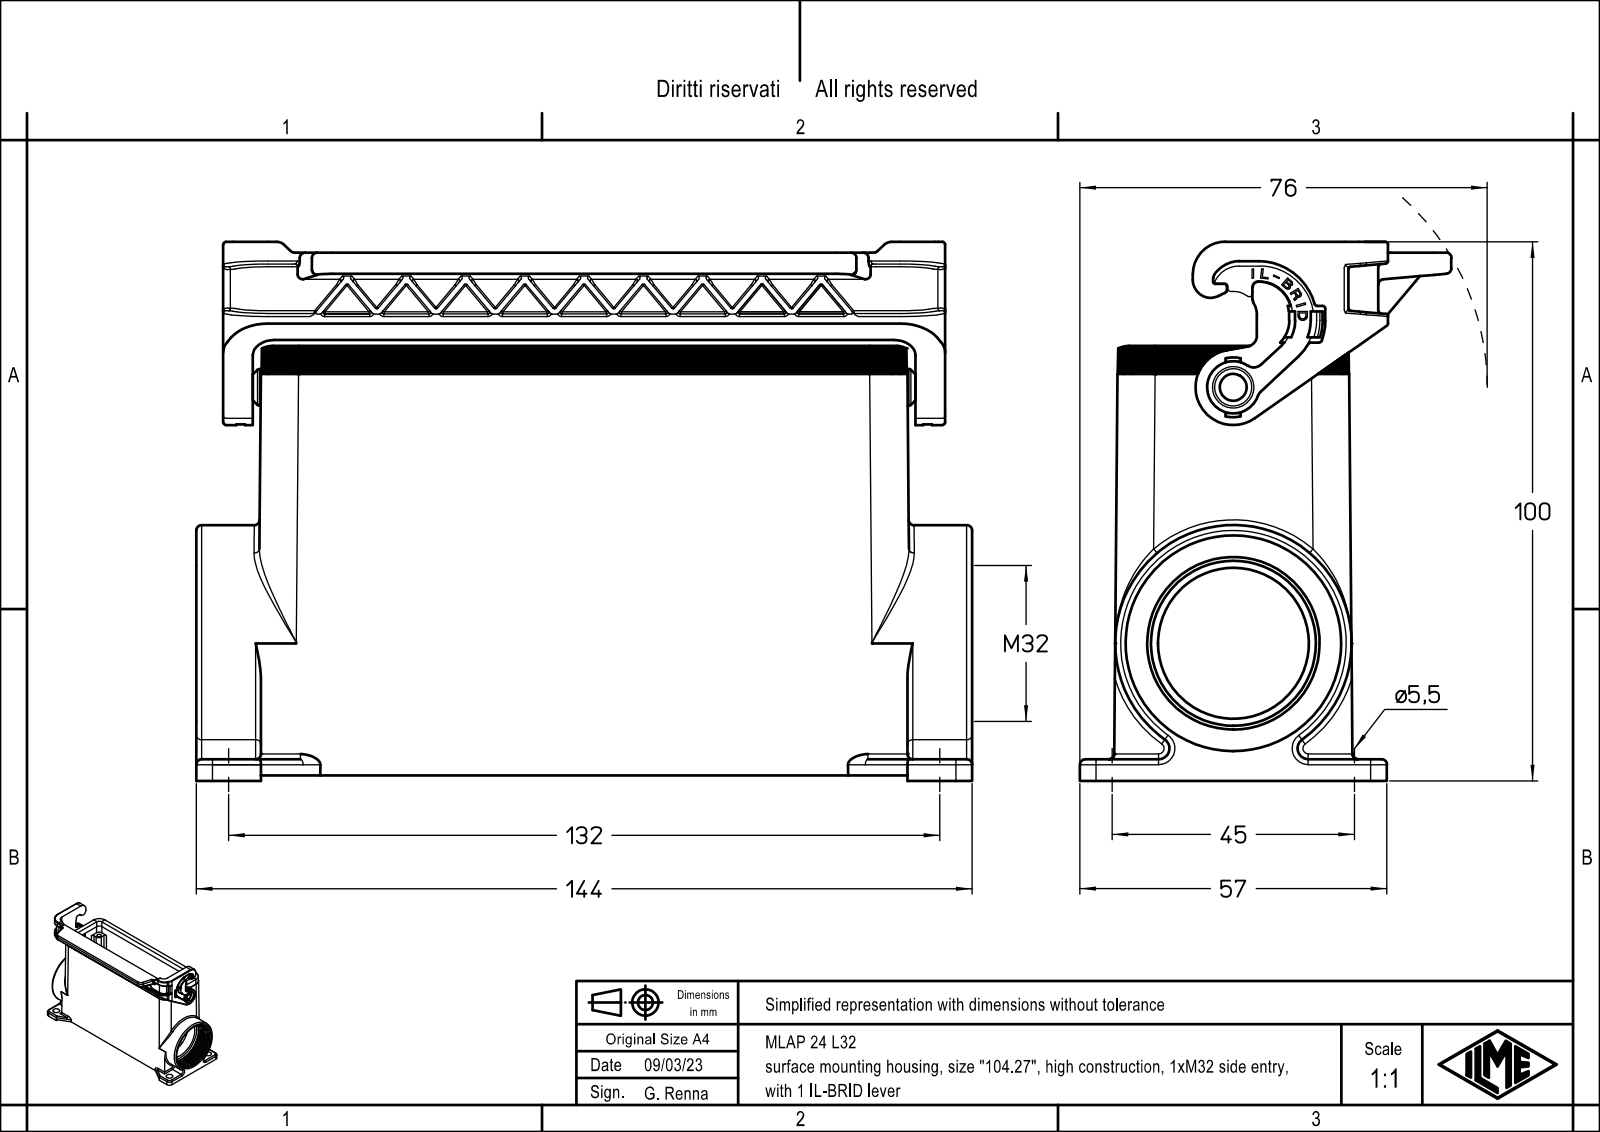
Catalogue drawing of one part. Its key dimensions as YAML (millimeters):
part_name: "MLAP 24 L40; MLAP 24 L32"
step_written_by: "Creo Elements/Direct Modeling 20.1B 02-Apr-2019 (C) Parametric Technology GmbH (AUTOMOTIVE_DESIGN)"
units: millimeters
bodies: {solids: 1, faces: 1039, planar: 651, cylindrical: 292, other: 96}
overall_size: [144, 100, 68.96]
volume: 177163
surface_area: 80841
round_holes:
  - {diameter: 3, count: 4}
  - {diameter: 3.5, count: 4}
  - {diameter: 5.5, count: 4}
  - {diameter: 3.25, count: 1}
  - {diameter: 5.4, count: 1}
  - {diameter: 7.7, count: 1}
  - {diameter: 28, count: 1}
  - {diameter: 30.5, count: 1}
round_bosses_or_shafts:
  - {diameter: 43.87, count: 1}
  - {diameter: 6.9, count: 1}
  - {diameter: 6.8, count: 1}
  - {diameter: 5.2, count: 1}
  - {diameter: 3.2, count: 1}
partial_cylinders:
  - {radius: 0.1, count: 27}
  - {radius: 1, count: 16}
  - {radius: 3, count: 16}
  - {radius: 0.2, count: 15}
  - {radius: 0.5, count: 11}
  - {radius: 2, count: 11}
  - {radius: 7, count: 10}
  - {radius: 1.5, count: 9}
face_to_face_distances: [3, 5.5, 97, 94, 4, 1, 7, 10.5, 133.5, 123]
hole_center_spacings: [16.64, 38.63, 118.34, 123.37, 27, 45, 104, 107.45]
